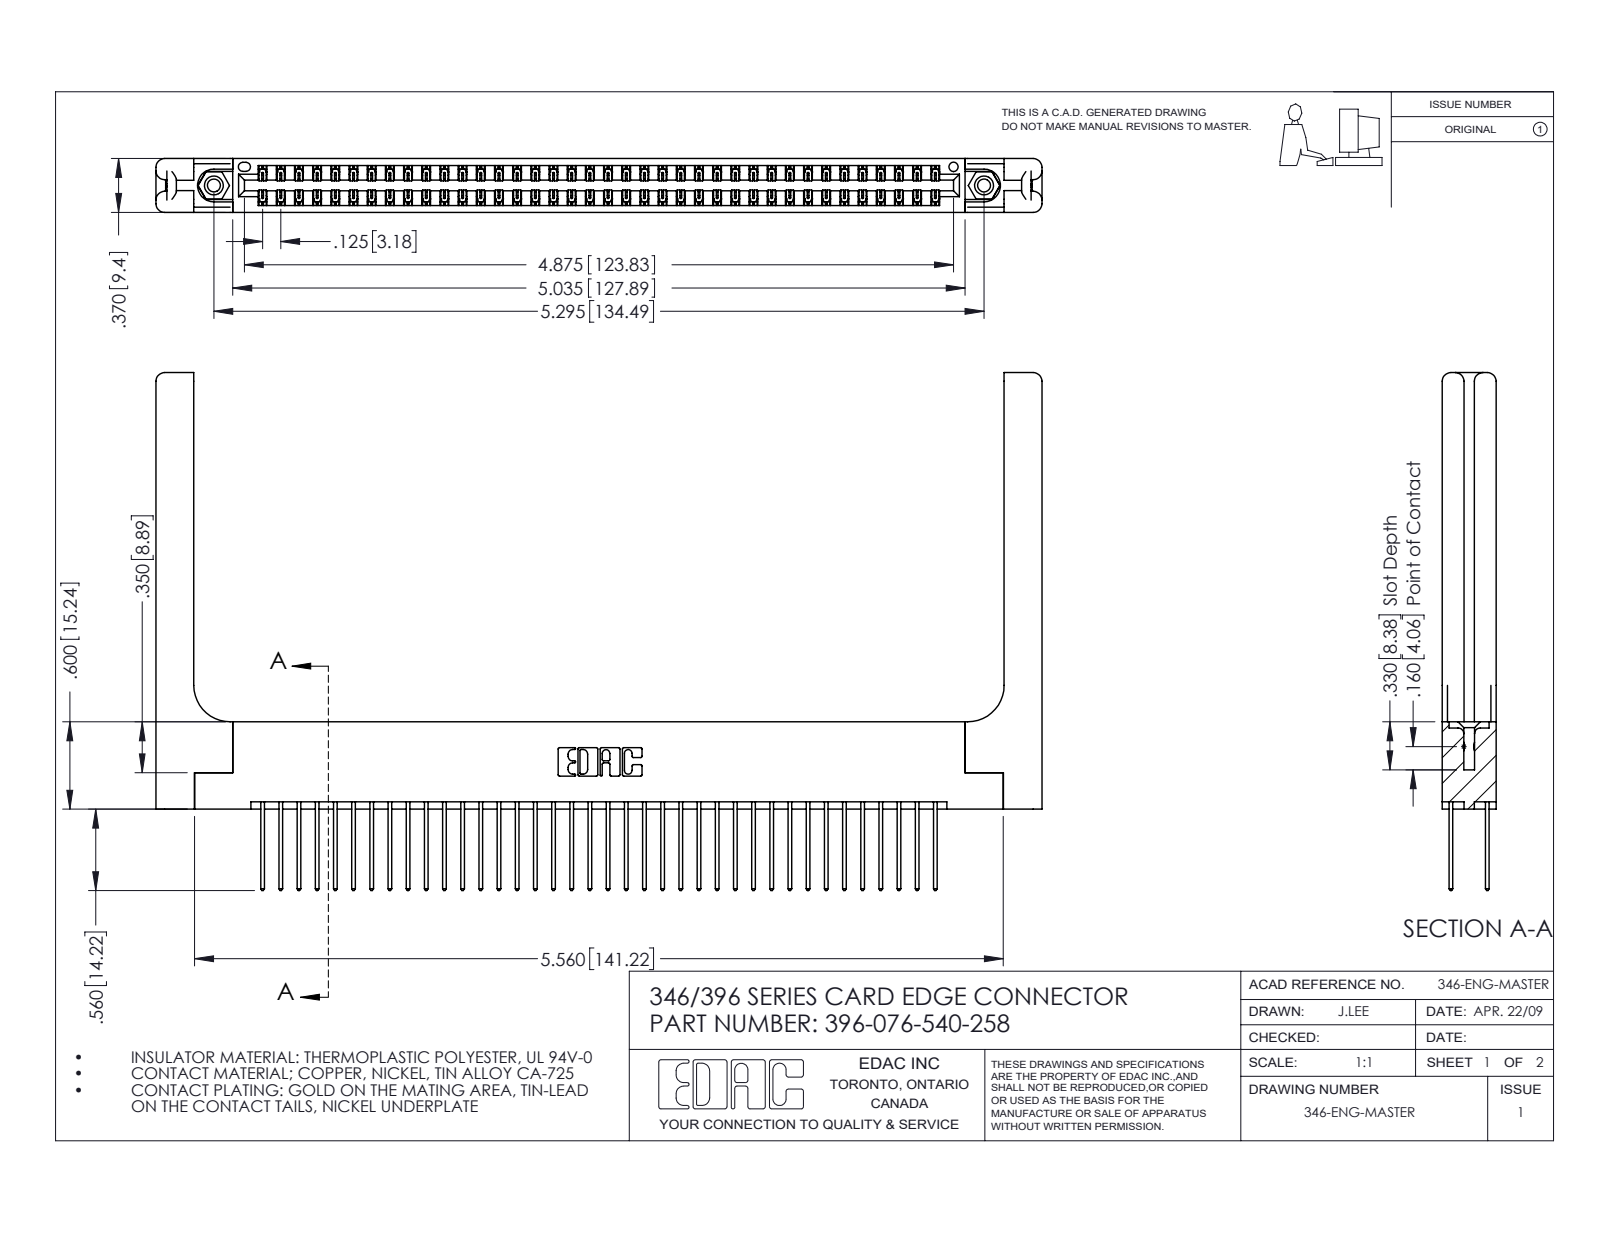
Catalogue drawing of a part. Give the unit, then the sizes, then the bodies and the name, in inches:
Units: inches
Overall size (bounding box): 6.091 × 3.56 × 0.37
Round holes (diameter × count): ⌀0.089 ×2, ⌀0.125 ×2, ⌀0.156 ×2, ⌀0.064 ×1
Round bosses / shafts (diameter × count): ⌀0.155 ×2
Partial cylindrical surfaces — rounded edges, fillets, slot ends (radius × count): R0.006 ×114, R0.01 ×76, R0.01 ×22, R0.06 ×16, R0.007 ×6, R0.031 ×6, R0.026 ×3, R0.014 ×2
Main face-to-face distances: 0.048, 0.322, 0.072, 0.37, 0.25, 0.025, 0.298, 0.148, 0.15, 0.275
Hole centre spacings: 0.246, 5.086, 5.295
Volume: 1.394 in³ · Surface area: 42.41 in²
Bodies: 81 solids, 4330 faces (2884 planar, 1386 cylindrical, 60 other)
Part name (STEP PRODUCT): 346-220-058_345-220-058; 396-076-540-258; 345-250-001_345-250-001-102; 345-292-001_345-293-140 (+1 more)
STEP written by: SolidWorks 2016 (CONFIG_CONTROL_DESIGN)
